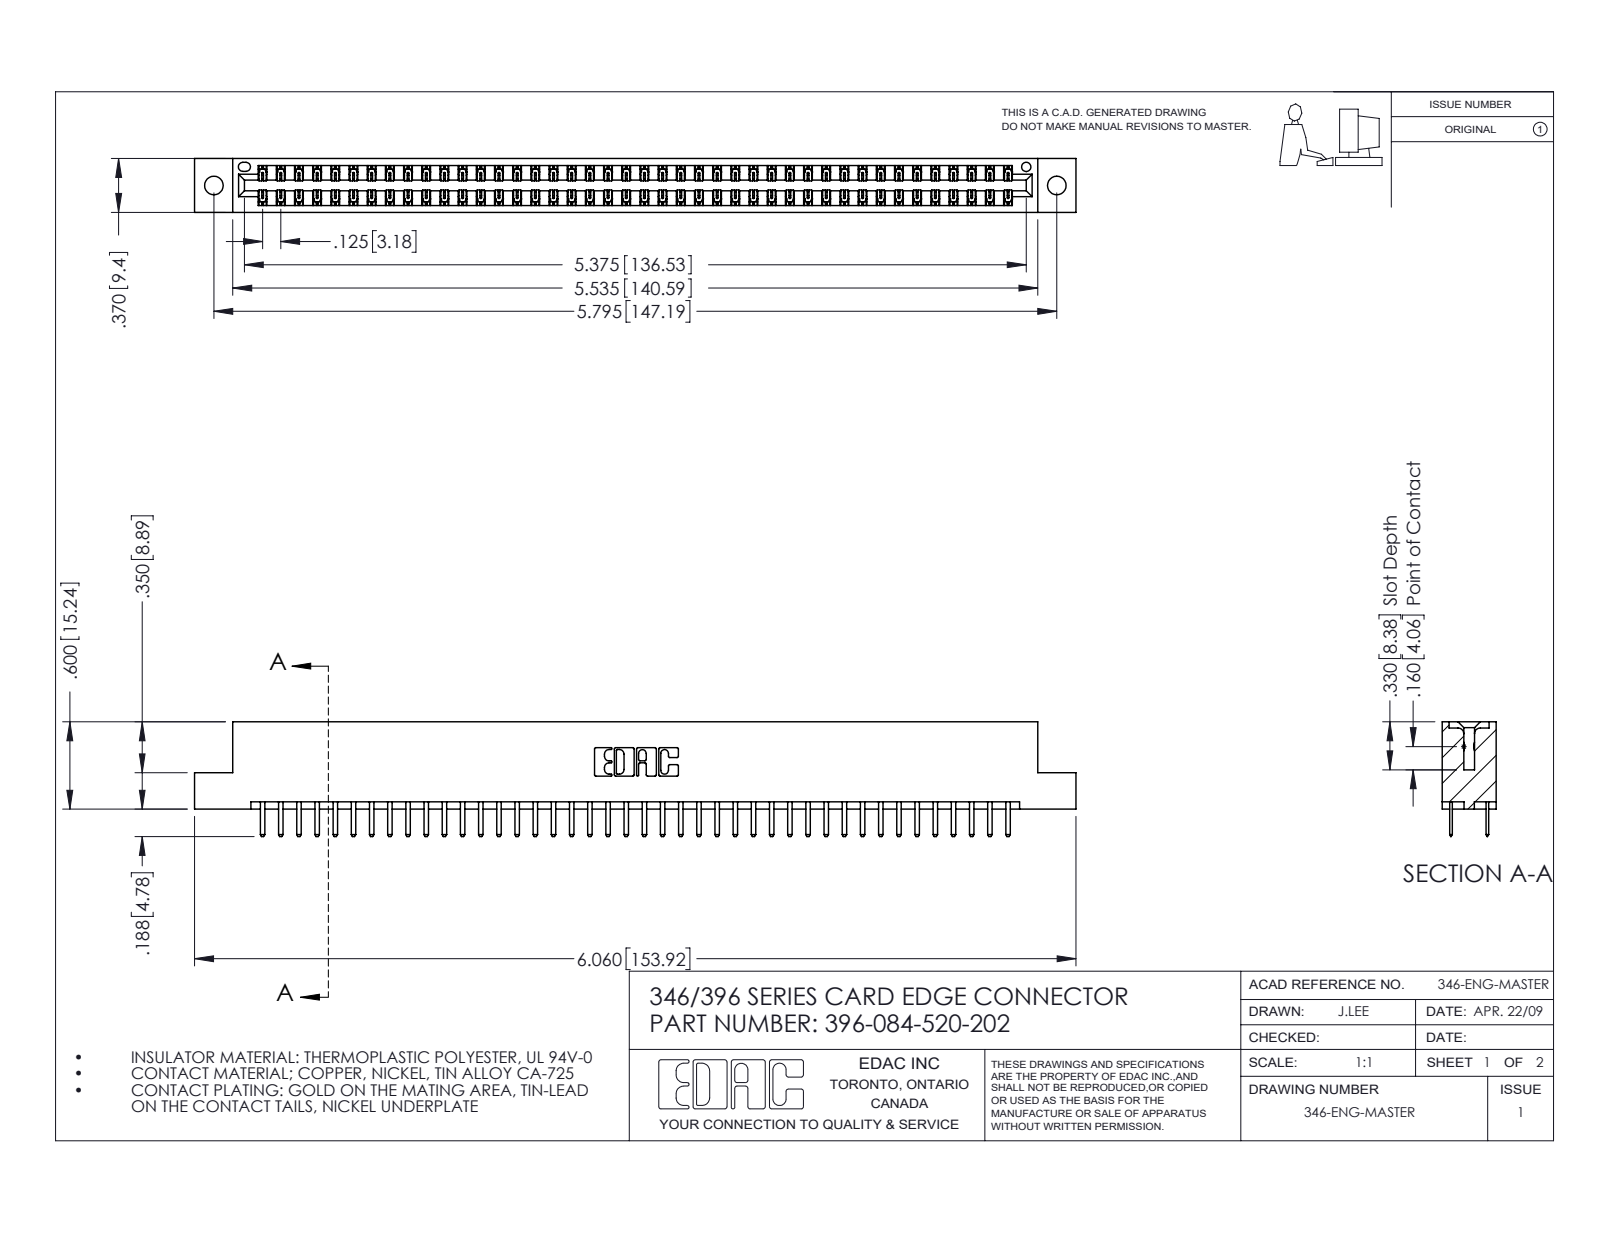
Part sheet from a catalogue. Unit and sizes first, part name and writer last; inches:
Units: inches
Overall size (bounding box): 6.06 × 0.788 × 0.37
Round holes (diameter × count): ⌀0.128 ×2, ⌀0.064 ×1
Partial cylindrical surfaces — rounded edges, fillets, slot ends (radius × count): R0.006 ×126, R0.01 ×88, R0.01 ×22, R0.007 ×6, R0.031 ×6, R0.026 ×3, R0.014 ×2, R0.022 ×2
Main face-to-face distances: 0.048, 0.322, 0.25, 0.37, 0.275, 0.072, 0.298, 0.025, 0.148, 0.222
Hole centre spacings: 0.246, 5.586, 5.795
Volume: 0.911 in³ · Surface area: 31.27 in²
Bodies: 85 solids, 4826 faces (3184 planar, 1642 cylindrical, 0 other)
Part name (STEP PRODUCT): 346 Part_Flush Mounting Lugs - 0.128 Dia; 396-084-520-202; 345-292-001_345-293-120
STEP written by: SolidWorks 2016 (CONFIG_CONTROL_DESIGN)
